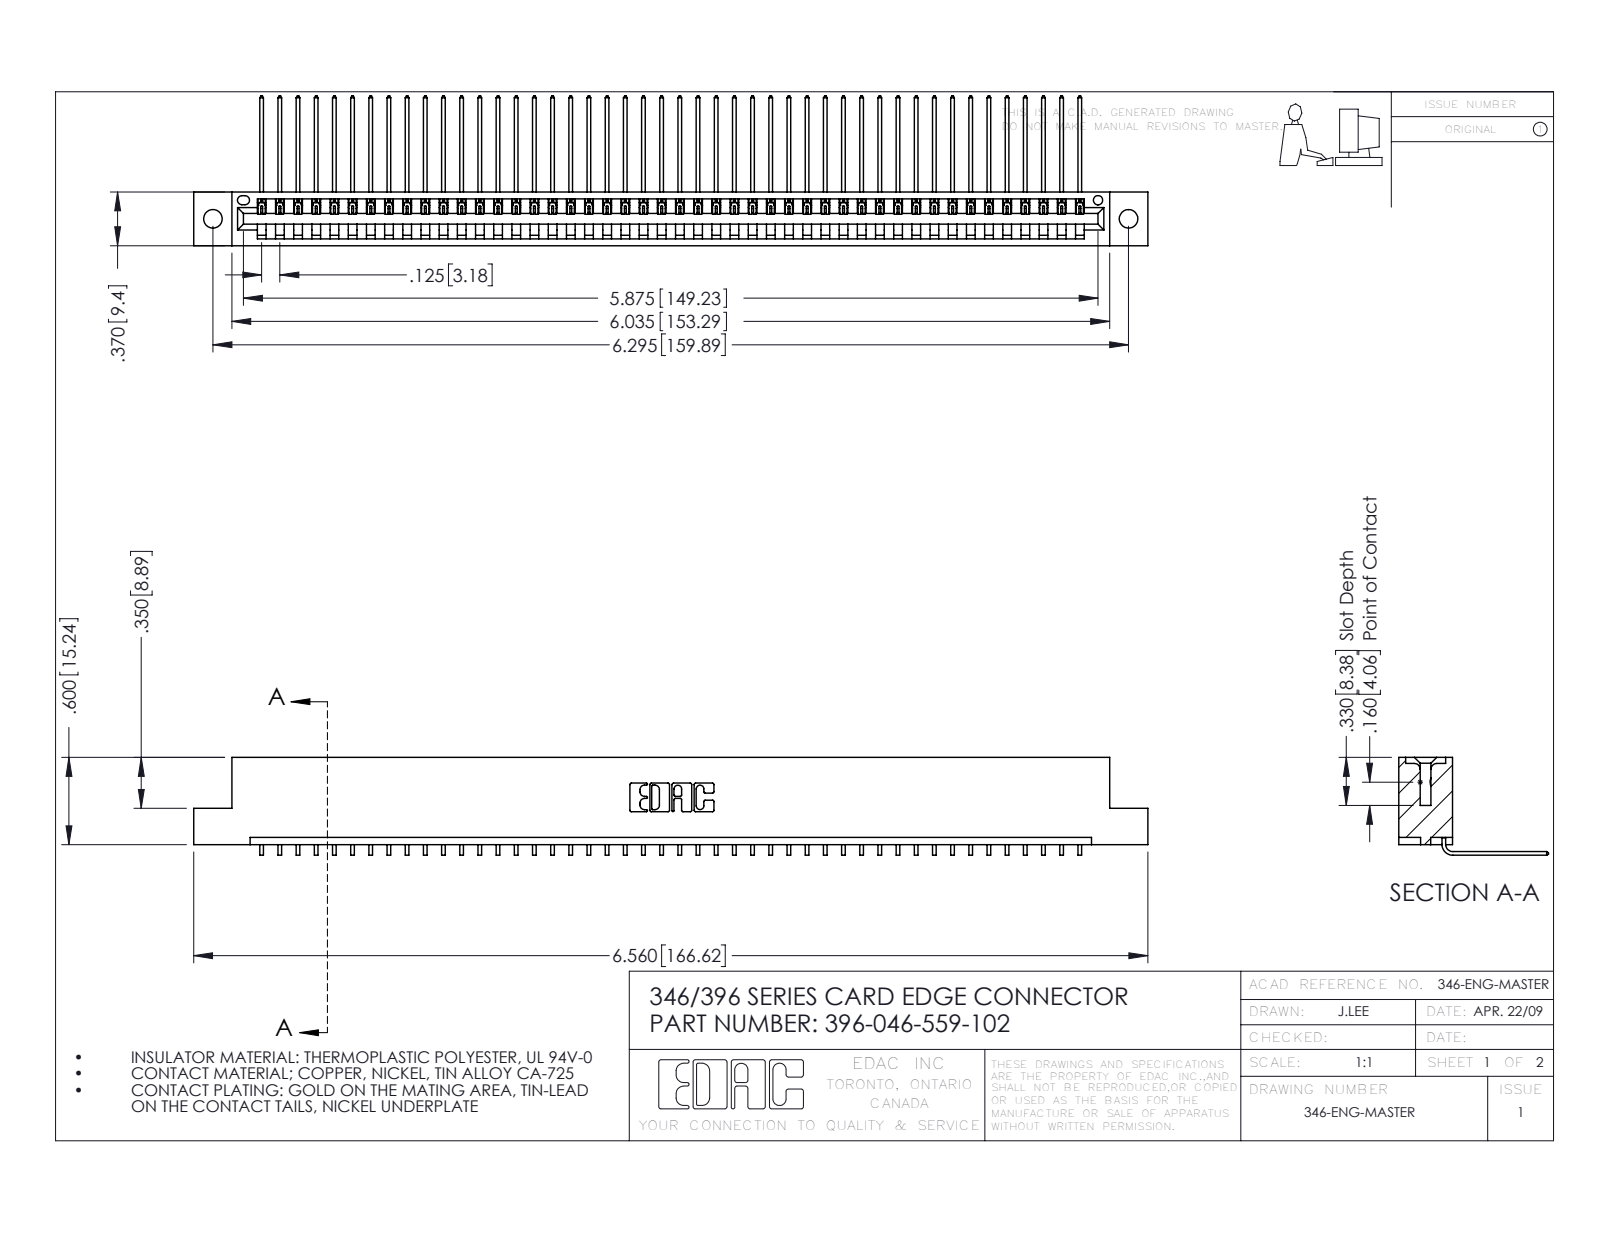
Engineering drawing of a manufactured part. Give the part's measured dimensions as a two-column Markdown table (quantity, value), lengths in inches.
| quantity | value |
| --- | --- |
| part name | 346 Part_Flush Mounting Lugs - 0.128 Dia; 345-292-001_558 559 Tail - 1; 396-046-559-102 |
| STEP written by | SolidWorks 2016 (CONFIG_CONTROL_DESIGN) |
| units | inches |
| bodies | 47 solids, 2882 faces (2008 planar, 874 cylindrical, 0 other) |
| overall size | 6.56 × 1.03 × 0.673 |
| volume | 0.982 in³ |
| surface area | 32.24 in² |
| round holes (diameter × count) | 0.128 × 2, 0.064 × 1 |
| partial cylindrical surfaces (radius × count) | 0.006 × 92, 0.01 × 22, 0.007 × 6, 0.031 × 6, 0.026 × 3, 0.031 × 2, 0.04 × 2, 0.014 × 1 |
| main face-to-face distances | 0.048, 0.322, 0.37, 0.025, 0.25, 0.072, 0.298, 0.148, 0.222, 0.1 |
| hole center spacings | 0.246, 6.086, 6.295 |
